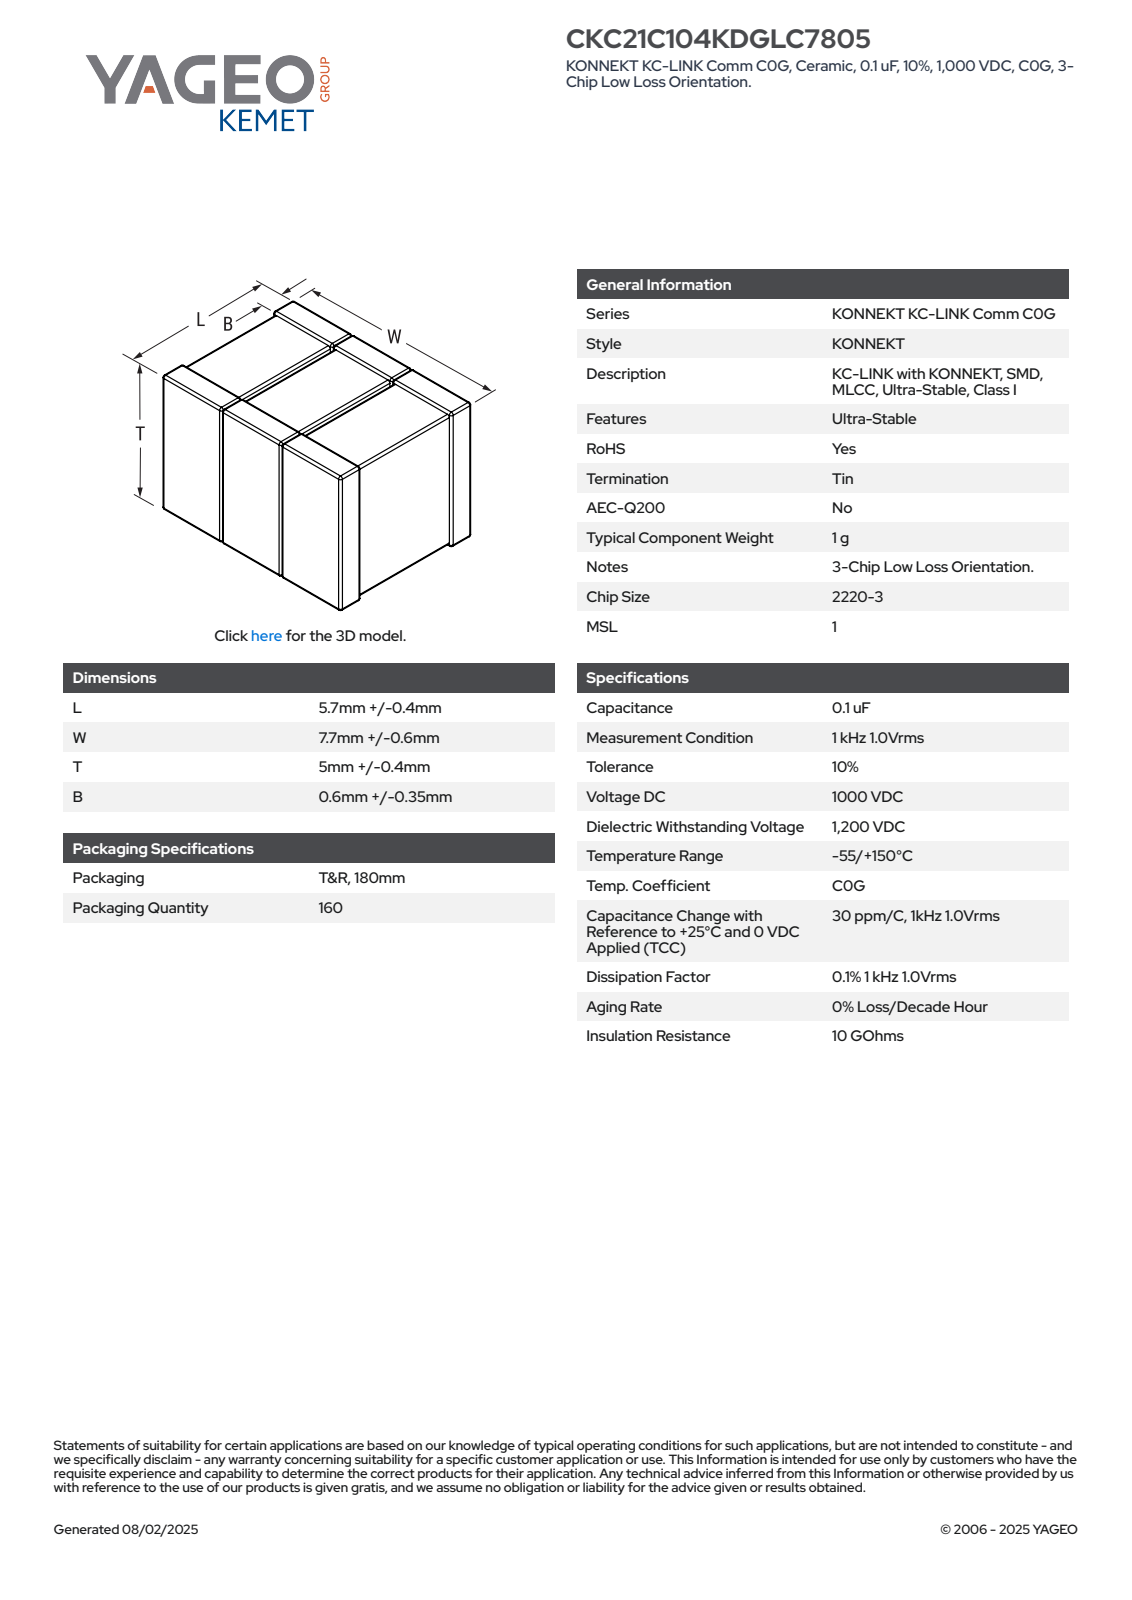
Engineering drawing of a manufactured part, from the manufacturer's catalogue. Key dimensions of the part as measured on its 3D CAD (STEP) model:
Part name (STEP PRODUCT): CCSS_K3LL_2220-3_L6.1W8.3B0.95T5.4
STEP written by: SolidWorks 2021 (AUTOMOTIVE_DESIGN)
Units: millimetres
Bodies: 12 solids, 351 faces (213 planar, 90 cylindrical, 48 other)
Overall size (bounding box): 8.3 × 6.1 × 5.4
Volume: 255 mm³ · Surface area: 385 mm²
Main face-to-face distances: 2.77, 5.53, 2.76, 2.68, 5.44, 2.59, 5.35, 6.1, 2.85, 2.67
